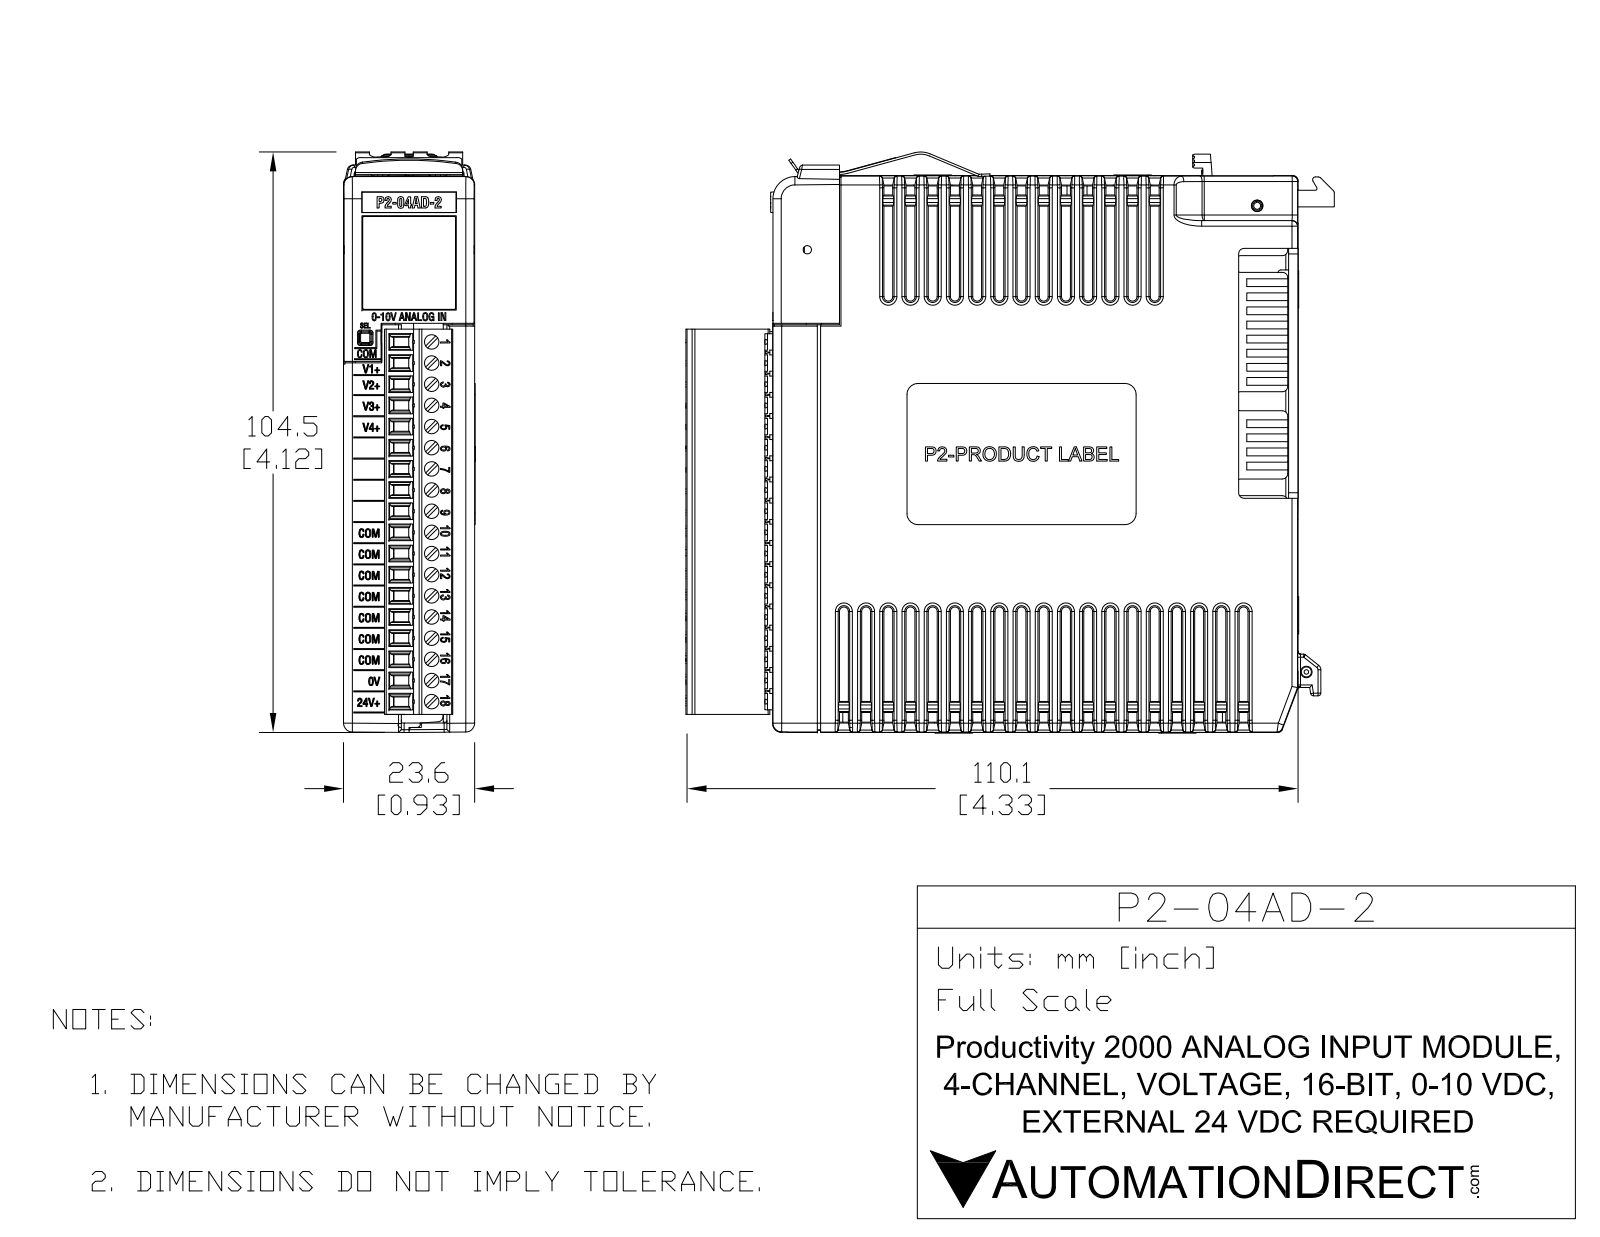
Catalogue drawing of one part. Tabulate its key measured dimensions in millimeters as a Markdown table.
| quantity | value |
| --- | --- |
| part name | P2-04AD-2 r1 Coord ext2 comb fXT fos wcb fXT |
| STEP written by | SolidWorks 2017 (AUTOMOTIVE_DESIGN) |
| units | millimeters |
| bodies | 4 solids, 4402 faces (3093 planar, 652 cylindrical, 657 other) |
| overall size | 104.6 × 104.4 × 24.4 |
| volume | 202 400 mm³ |
| surface area | 45 750 mm² |
| round holes (diameter × count) | 1.2 × 2, 1.5 × 1 |
| round bosses / shafts (diameter × count) | 0.4 × 4, 0.7 × 1 |
| partial cylindrical surfaces (radius × count) | 0.5 × 173, 0.2 × 130, 1 × 74, 1.6 × 33, 1.5 × 23, 0.6 × 20, 1.6 × 15, 1.6 × 13 |
| main face-to-face distances | 23.6, 4.1, 19.6, 2.4, 9.4, 1.6, 22, 3.8, 5.3, 12.6 |
| hole center spacings | 15.7 |
